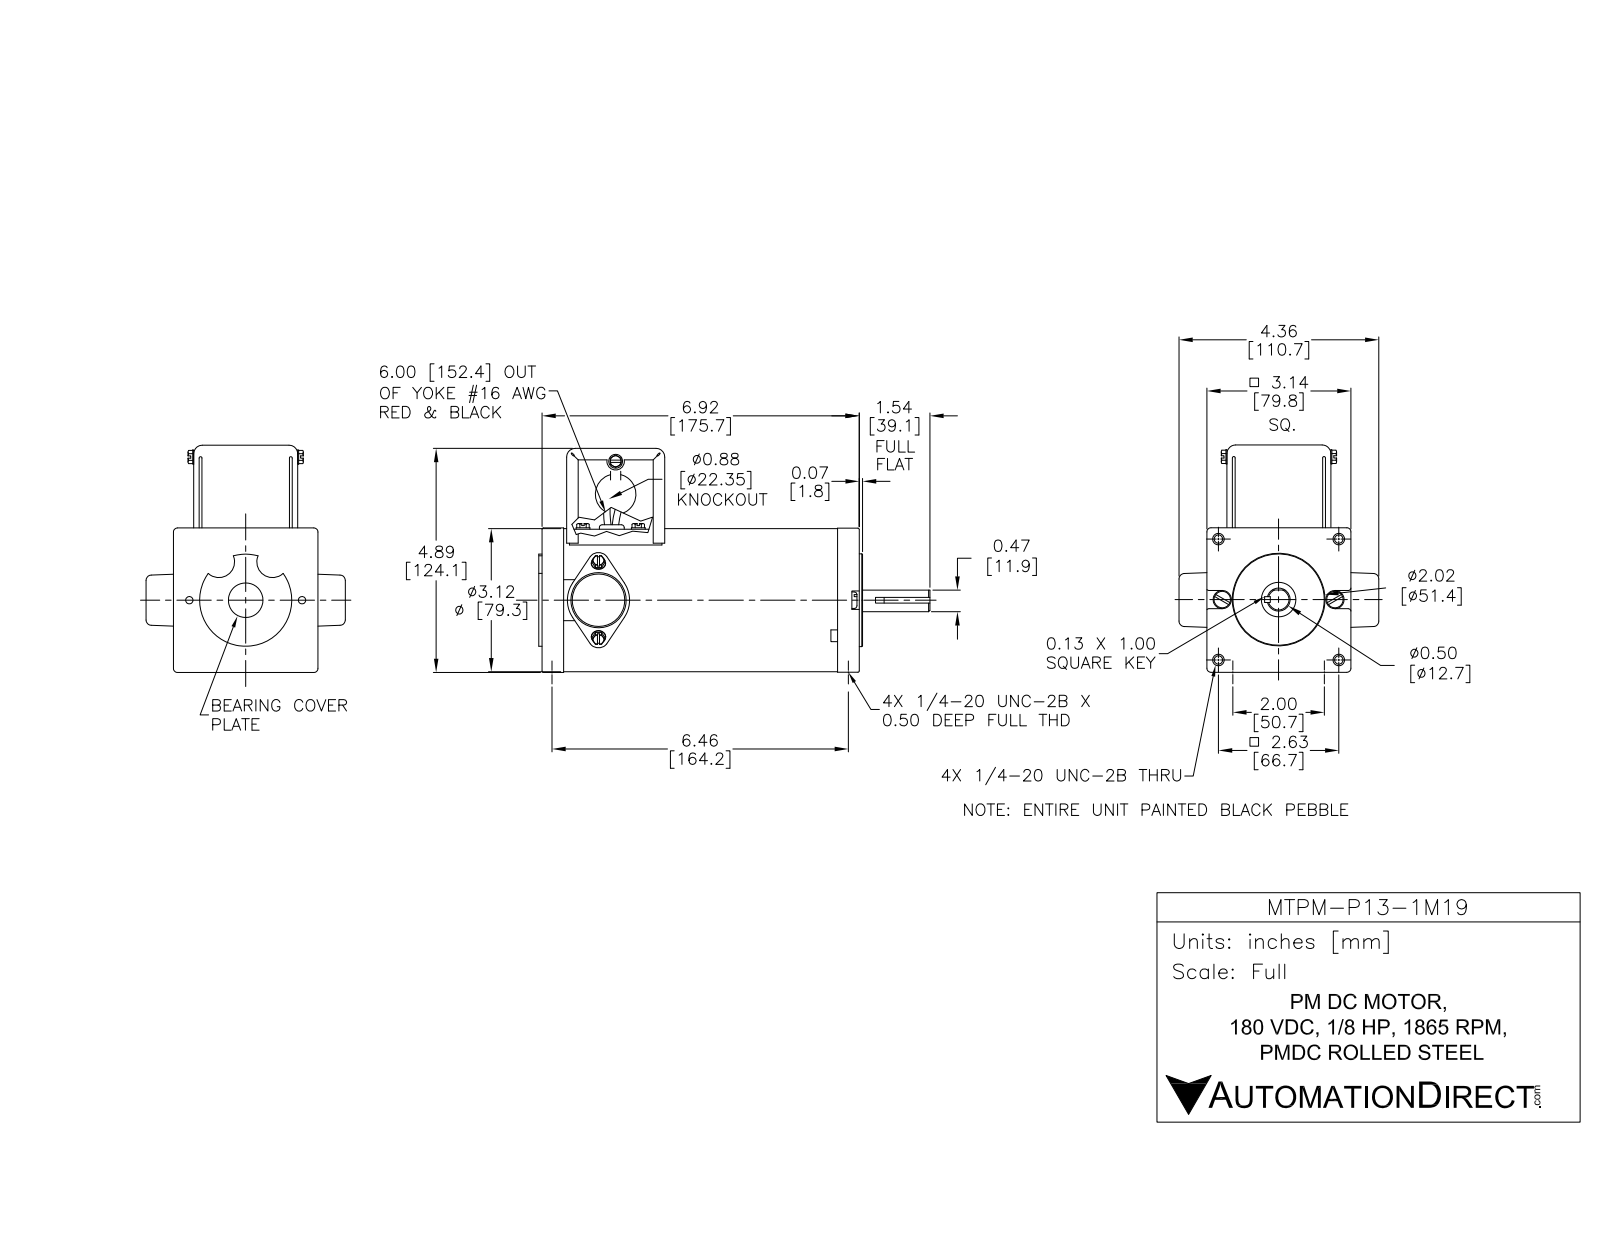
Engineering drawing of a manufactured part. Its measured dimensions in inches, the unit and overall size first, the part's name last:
Units: inches
Overall size (bounding box): 8.52 × 4.944 × 4.39
Round holes (diameter × count): ⌀0.125 ×4, ⌀0.198 ×2, ⌀0.25 ×1, ⌀0.3 ×1, ⌀0.375 ×1, ⌀0.5 ×1, ⌀1.225 ×1, ⌀2.2 ×1, ⌀3 ×1, ⌀3.125 ×1
Round bosses / shafts (diameter × count): ⌀0.3 ×4, ⌀0.125 ×2, ⌀0.1 ×2, ⌀0.625 ×1, ⌀0.301 ×1
Partial cylindrical surfaces — rounded edges, fillets, slot ends (radius × count): R0.191 ×4, R0.234 ×4, R0.159 ×2, R0.341 ×2, R0.613 ×1, R0.667 ×1, R0.678 ×1, R1 ×1
Main face-to-face distances: 0.031, 0.25, 0.063, 6.665, 2.135, 6.415, 2.047, 0.094, 2.198, 6.915
Hole centre spacings: 1.318, 1.859, 2.63, 2.865, 1.23, 3.719, 2.46, 3.083
Volume: 13.76 in³ · Surface area: 273.7 in²
Bodies: 28 solids, 409 faces (271 planar, 113 cylindrical, 25 other)
Part name (STEP PRODUCT): MTPM-P13-1M19
STEP written by: SolidWorks 2017 (AUTOMOTIVE_DESIGN)
